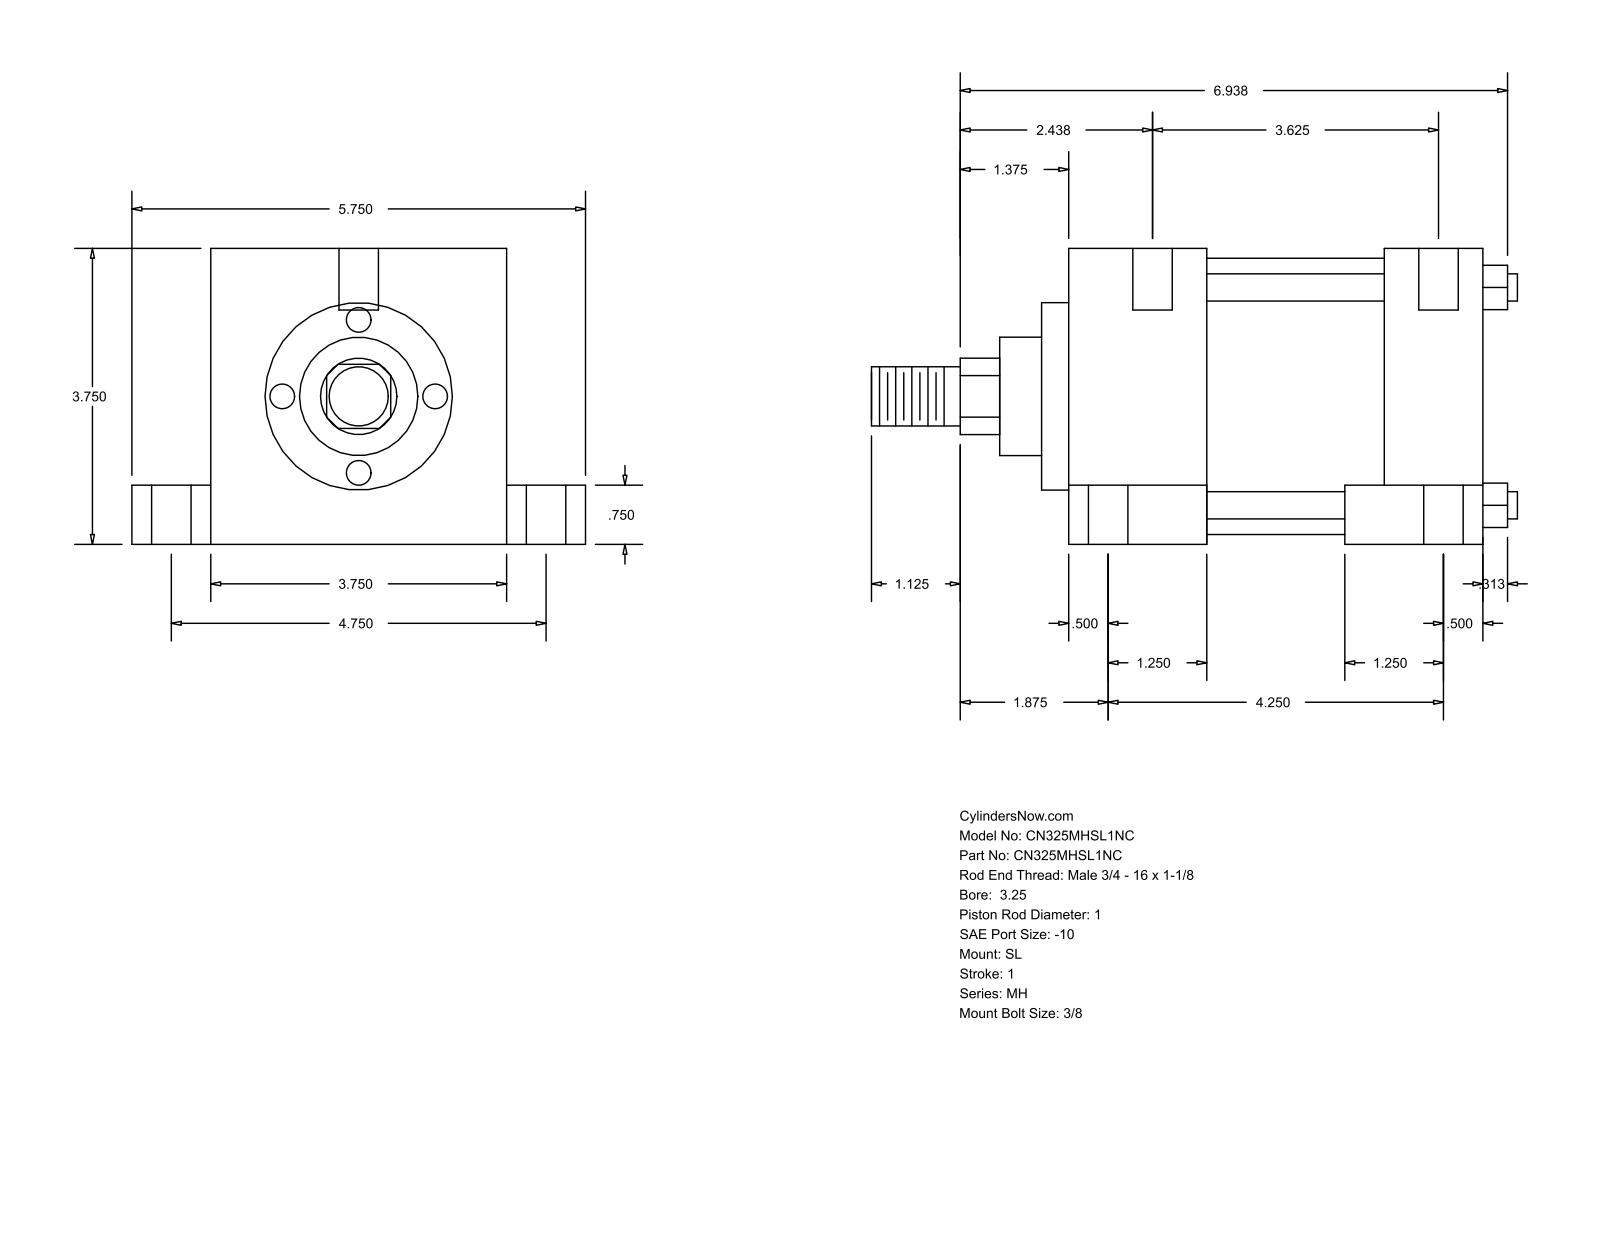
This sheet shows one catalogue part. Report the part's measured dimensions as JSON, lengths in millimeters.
{"part_name": "MH_SL__0325_1", "step_written_by": "GSSL Pune (CONFIG_CONTROL_DESIGN)", "units": "millimeters", "bodies": {"solids": 0, "faces": 110, "planar": 77, "cylindrical": 33, "other": 0}, "overall_size": [207.96, 146.05, 95.25], "round_holes": [[12.7, 6], [5.56, 4], [19.05, 4]], "round_bosses_or_shafts": [[8.76, 4], [88.9, 1], [60.33, 1], [38.1, 1], [25.4, 1], [19.05, 1]], "partial_cylinders_radius": [[12.29, 1]], "face_to_face_distances": [95.24, 133.36, 44.46, 88.9, 25.41, 120.65, 19.05, 76.19, 101.61, 57.15], "hole_center_spacings": [60.35, 60.41, 61.65, 62, 98.42, 107.95, 111.41, 112.74]}
